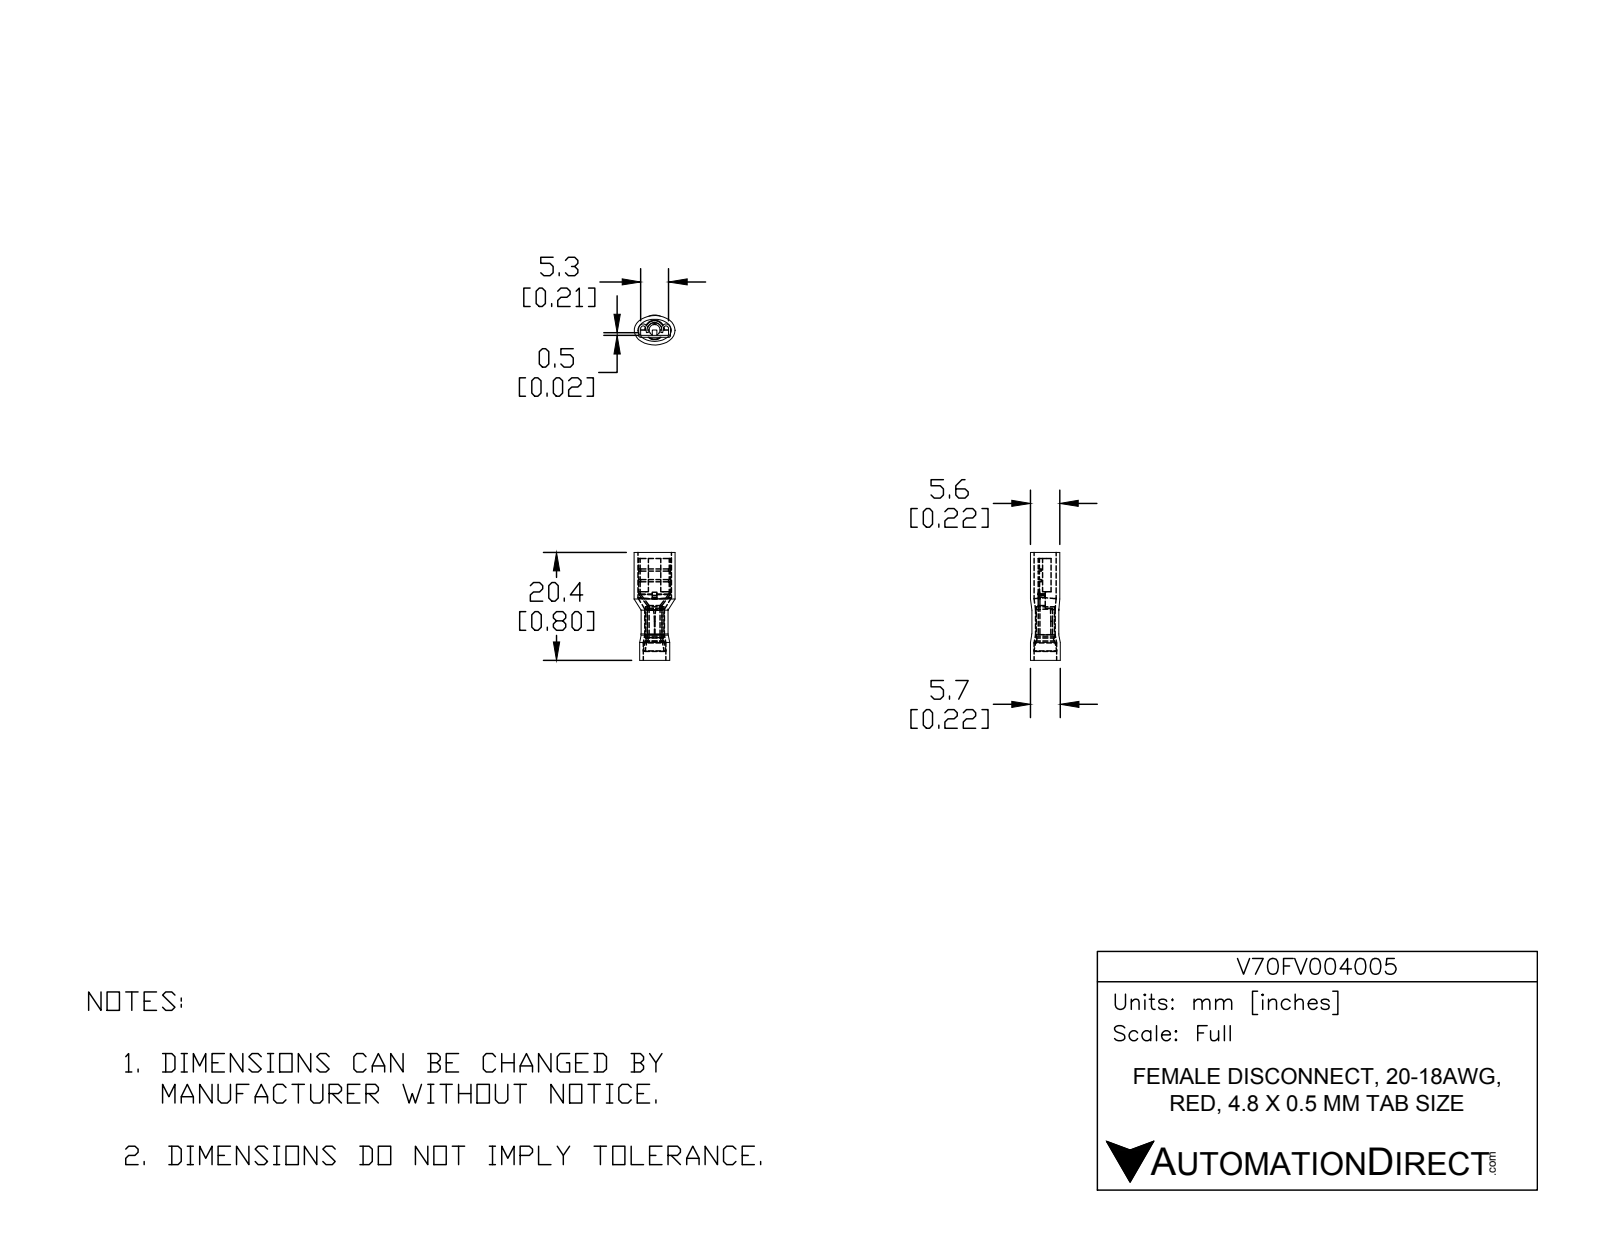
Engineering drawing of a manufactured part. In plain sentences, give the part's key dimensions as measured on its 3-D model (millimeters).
The part is named "V70FV004005". Its 3-D file was written by "SolidWorks 2017 (AUTOMOTIVE_DESIGN)". It is 3 solids with 127 faces: 51 planar, 36 cylindrical and 40 other. Overall it measures 20.44 by 7.73 by 5.68 millimeters. Its volume is 318 cubic millimeters and its surface area 1 201 square millimeters. Round holes: 1 of diameter 2.05, 1 of diameter 2.78, 1 of diameter 3.7, 1 of diameter 4.28. Round bosses or shafts: 1 of diameter 5.68, 1 of diameter 5.1, 1 of diameter 3.48, 1 of diameter 2.75. Partial cylindrical surfaces (rounded edges, fillets, slot ends): 2 of radius 0.12, 2 of radius 0.25, 2 of radius 0.49, 2 of radius 0.84, 2 of radius 15.72, 1 of radius 0.29, 1 of radius 0.64. The main face-to-face distances are 0.35, 5.65, 20.44, 6, 5.3, 2, 2.4, 19.3, 1.14, 0.4.
